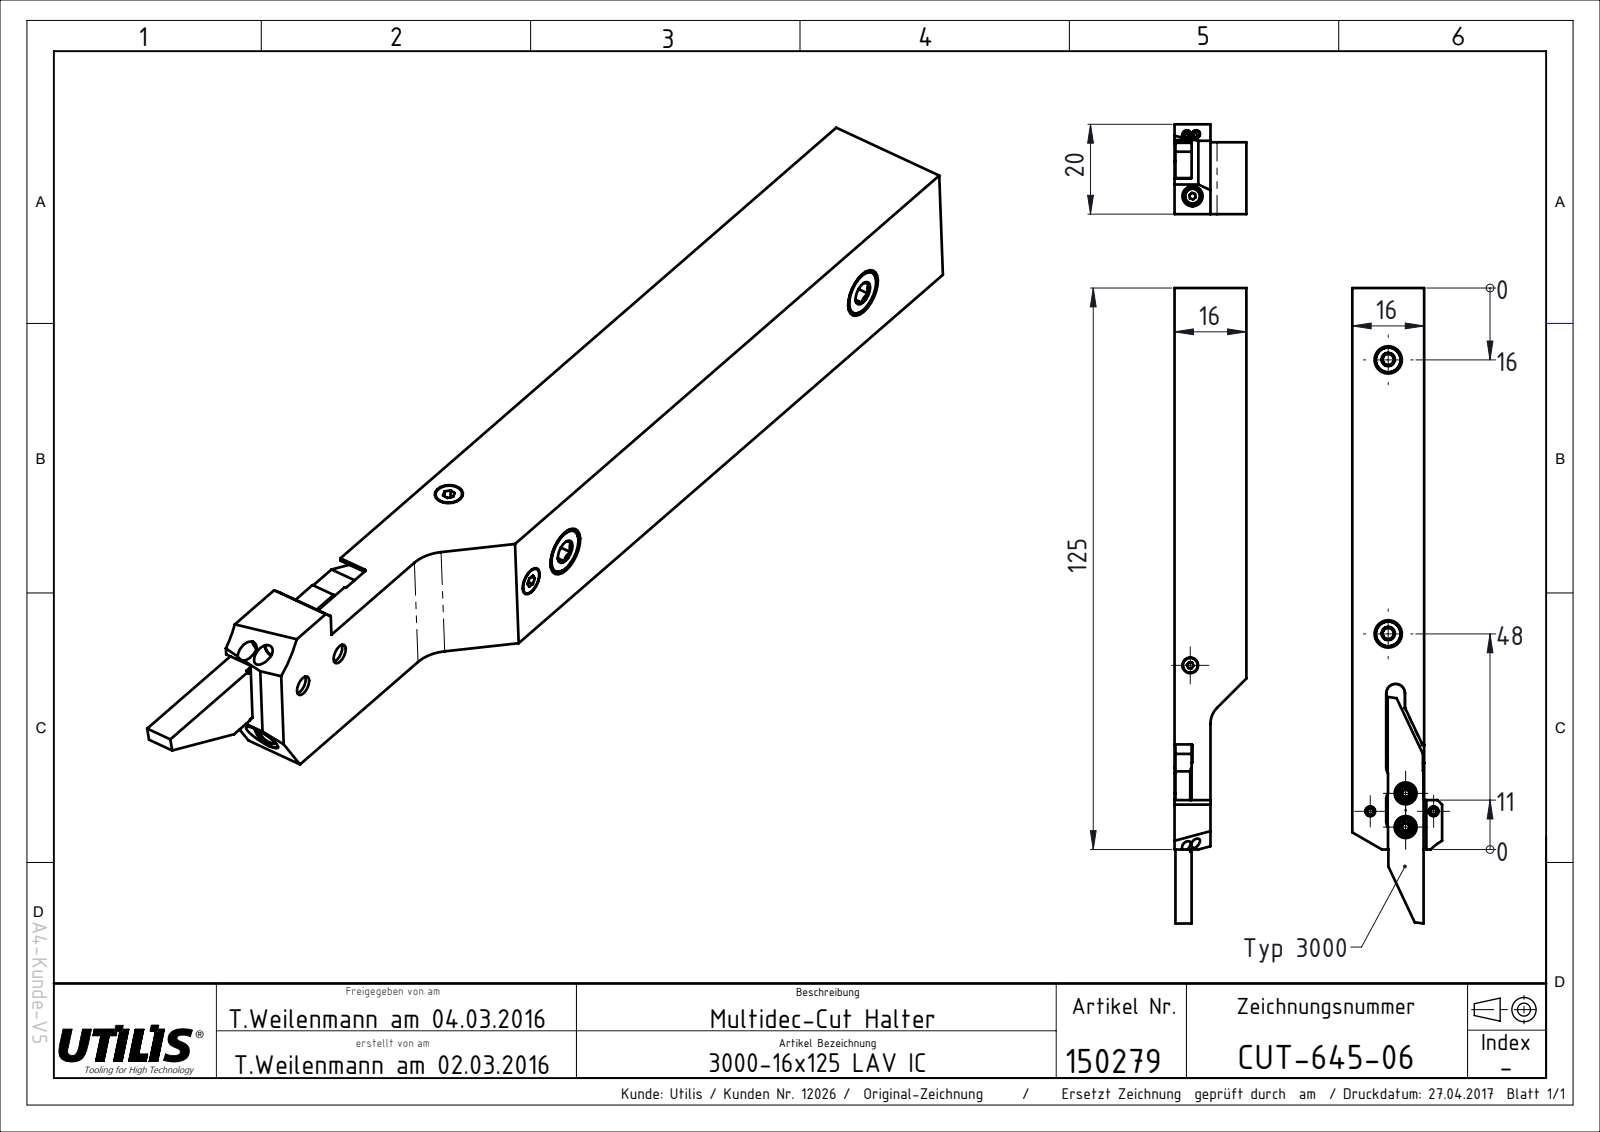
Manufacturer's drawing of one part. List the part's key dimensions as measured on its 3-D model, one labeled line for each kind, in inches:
Part name (STEP PRODUCT): CUT-645-06
STEP written by: SolidWorks 2016 (AUTOMOTIVE_DESIGN)
Units: inches
Bodies: 1 solid, 125 faces (54 planar, 45 cylindrical, 26 other)
Overall size (bounding box): 5.274 × 0.787 × 0.63
Volume: 1.694 in³ · Surface area: 13.47 in²
Round holes (diameter × count): ⌀0.14 ×2
Round bosses / shafts (diameter × count): ⌀0.161 ×1, ⌀0.118 ×1
Partial cylindrical surfaces — rounded edges, fillets, slot ends (radius × count): R0.008 ×13, R0.018 ×6, R0.083 ×5, R0.012 ×2, R0.006 ×1, R0.02 ×1, R0.197 ×1, R0.394 ×1
Main face-to-face distances: 0.63, 0.315, 0.622, 0.307, 0.157, 0.15, 0.165, 0.142, 0.48, 0.625
Hole centre spacings: 0.295
